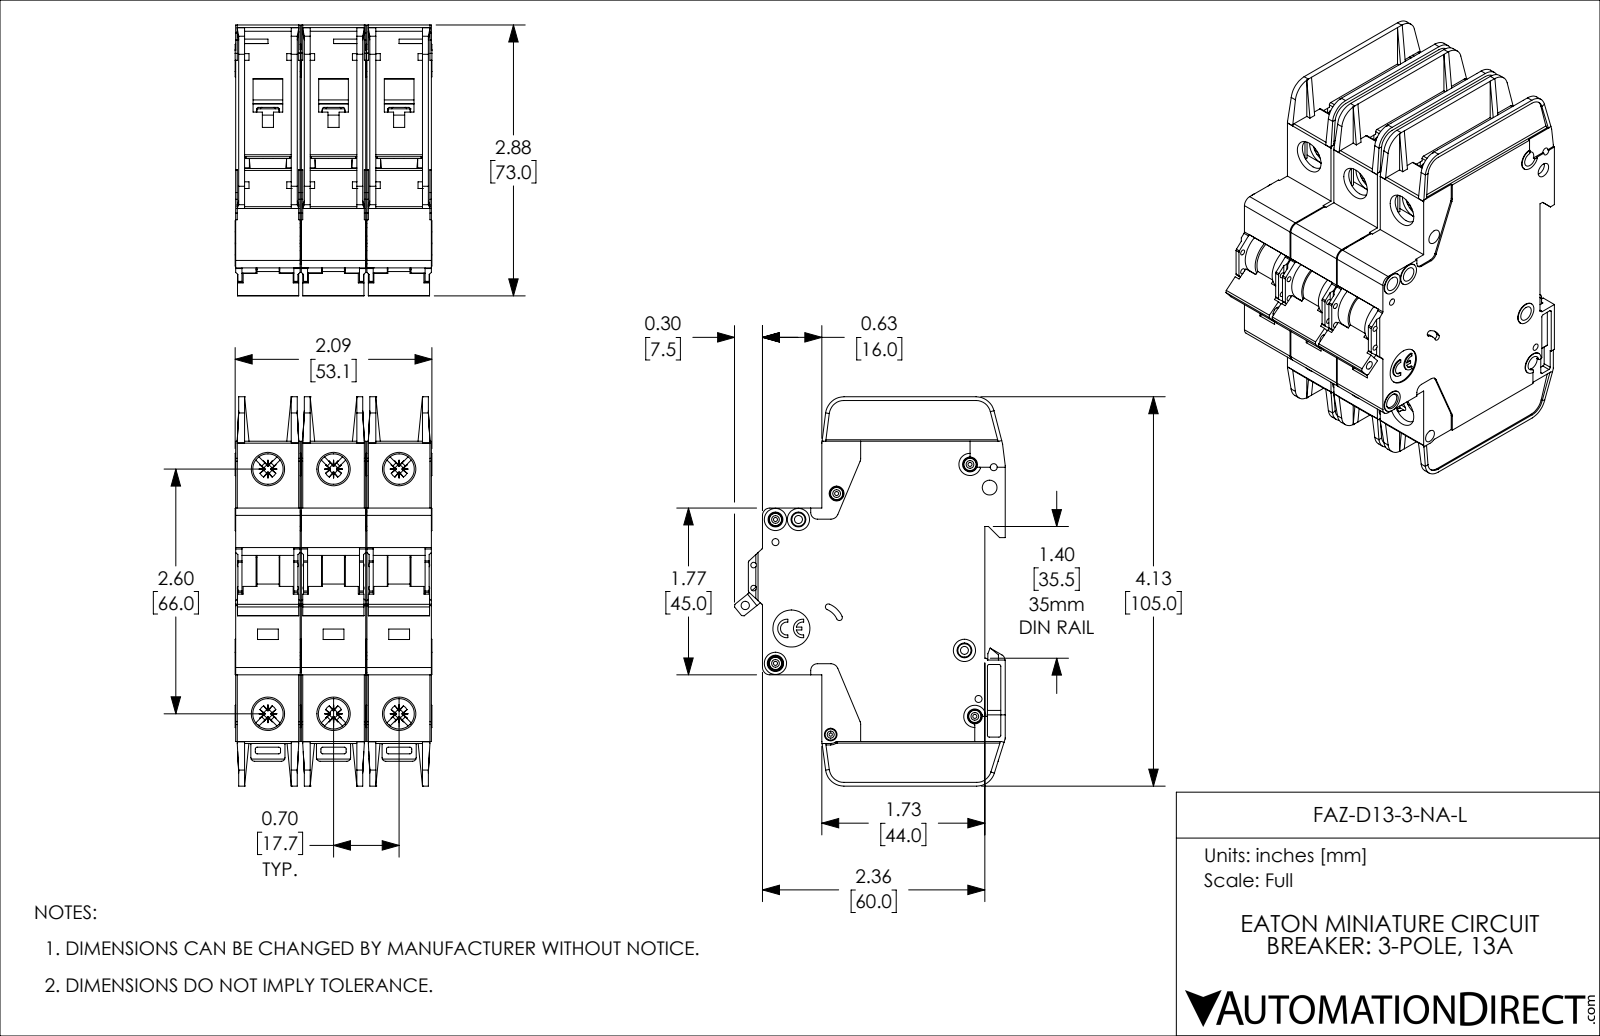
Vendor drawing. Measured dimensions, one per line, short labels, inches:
name: FAZ-D13-3-NA-L
written by: SolidWorks 2019 (AUTOMOTIVE_DESIGN)
unit: in
bodies: 3 solids, 3381 faces (2013 planar, 1071 cylindrical, 297 other)
size: 4.134 × 2.876 × 2.091
volume: 14.05 in³; area: 123 in²
holes: 8× ⌀0.157, 6× ⌀0.323, 5× ⌀0.043, 4× ⌀0.075, 2× ⌀0.059, 2× ⌀0.085, 1× ⌀0.035, 1× ⌀0.089, 1× ⌀0.098, 1× ⌀0.134, 1× ⌀0.394
bosses: 5× ⌀0.13, 4× ⌀0.236, 4× ⌀0.118, 3× ⌀0.098
rounds: 72× R0.02, 30× R0.016, 18× R0.039, 12× R0.043, 12× R0.079, 6× R0.008, 6× R0.01, 6× R0.028
face distances: 0.697, 0.047, 1.394, 0.685, 0.591, 1.382, 0.744, 0.65, 0.106, 0.094
hole spacings: 0.697, 2.69, 2.598, 0.244, 0.537, 0.87, 1.394, 2.948
